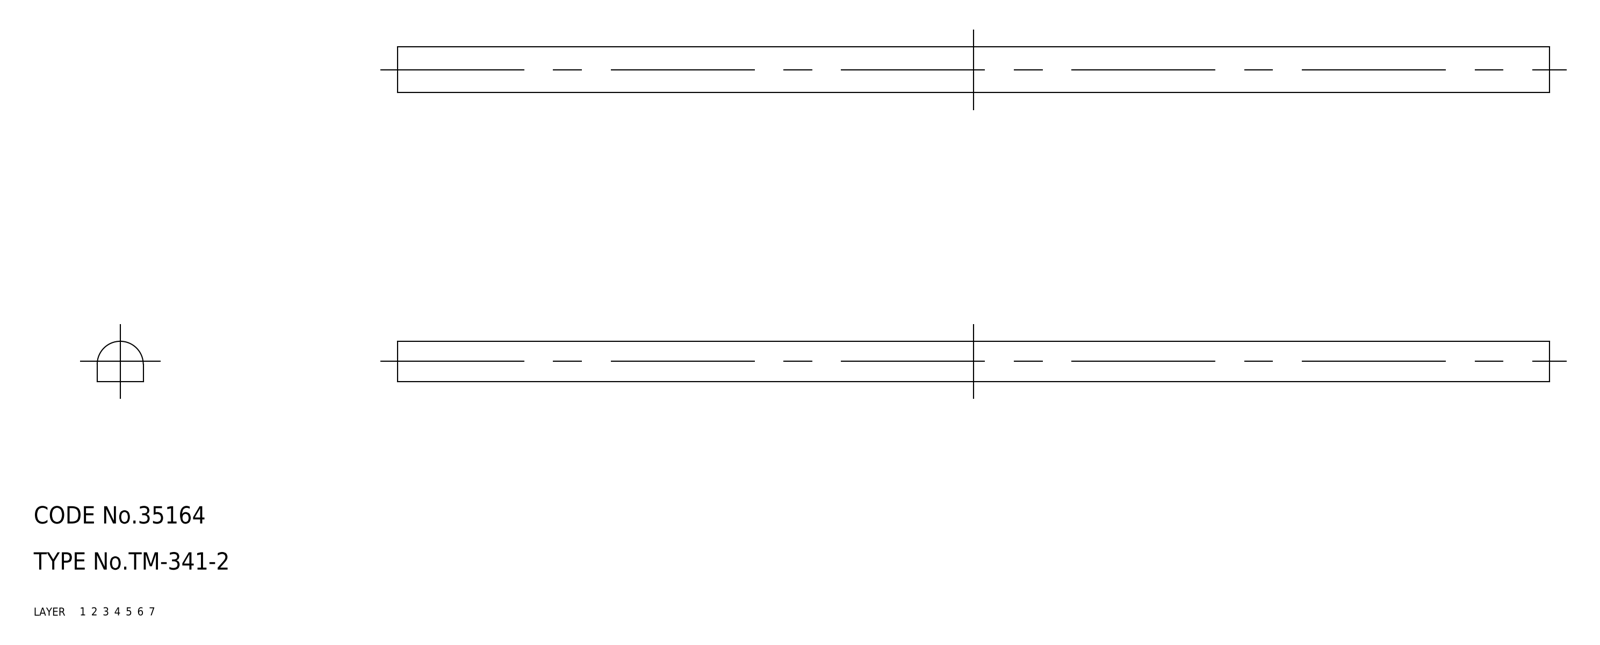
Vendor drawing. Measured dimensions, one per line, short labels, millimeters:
name: TM_341_2; rubber foam
written by: SolidWorks 2015 (AUTOMOTIVE_DESIGN)
unit: mm
bodies: 1 solid, 6 faces (5 planar, 1 cylindrical, 0 other)
size: 200 × 8 × 7
volume: 9 827 mm³; area: 5 412 mm²
rounds: 1× R4
face distances: 8, 200
